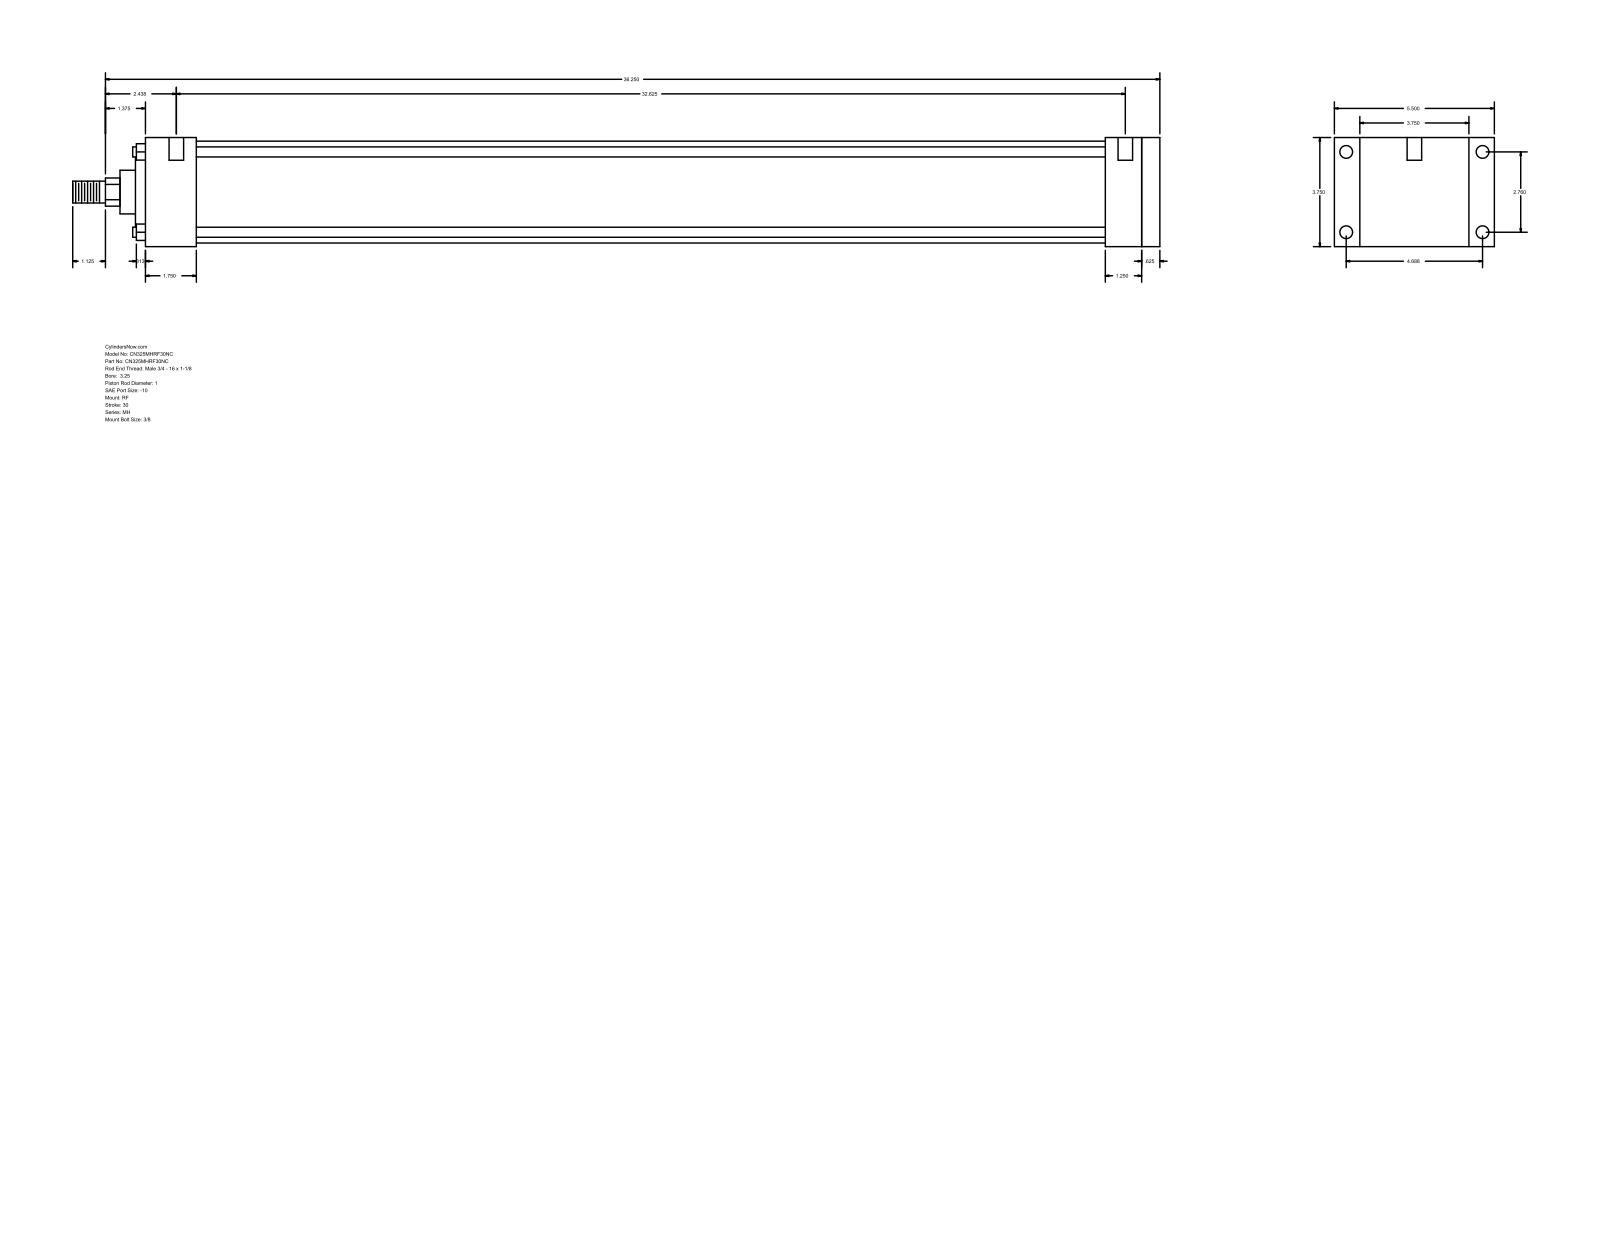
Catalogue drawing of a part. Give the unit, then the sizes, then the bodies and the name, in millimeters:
Units: millimetres
Overall size (bounding box): 949.33 × 139.7 × 95.25
Round holes (diameter × count): ⌀5.56 ×4, ⌀11.13 ×4, ⌀12.7 ×2
Round bosses / shafts (diameter × count): ⌀8.76 ×4, ⌀88.9 ×1, ⌀60.33 ×1, ⌀38.1 ×1, ⌀25.4 ×1, ⌀19.05 ×1
Partial cylindrical surfaces — rounded edges, fillets, slot ends (radius × count): R12.29 ×1
Main face-to-face distances: 95.24, 885.83, 869.96, 15.87, 22.23, 117.47, 44.46, 825.5, 841.37, 838.2
Hole centre spacings: 70.1, 119.06, 138.16, 835.02, 1.58, 4.76, 828.68, 830.26
Bodies: 0 solids, 94 faces (65 planar, 29 cylindrical, 0 other)
Part name (STEP PRODUCT): MH_RF__0325_1
STEP written by: GSSL Pune (CONFIG_CONTROL_DESIGN)
